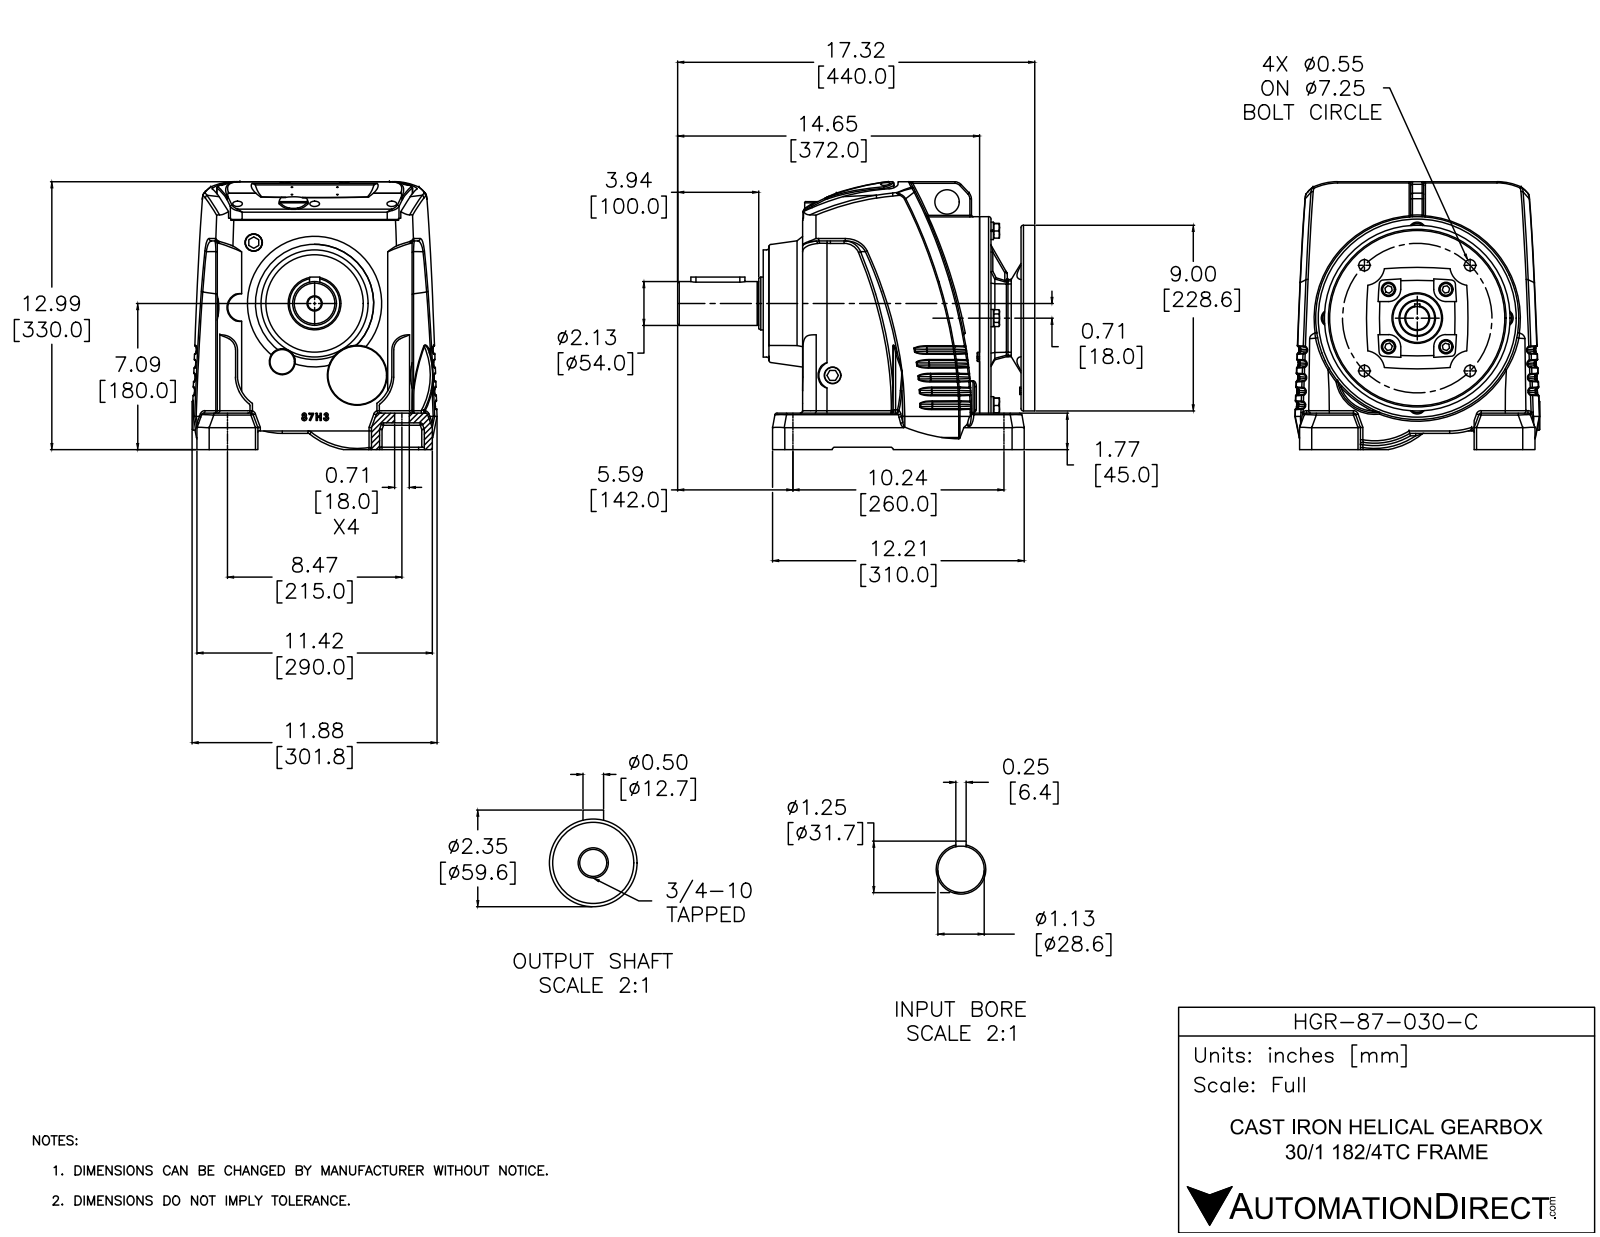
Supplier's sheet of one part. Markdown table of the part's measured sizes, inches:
| quantity | value |
| --- | --- |
| part name | HGR-87-020-C |
| STEP written by | SolidWorks 2015 (CONFIG_CONTROL_DESIGN) |
| units | inches |
| bodies | 27 solids, 1305 faces (317 planar, 298 cylindrical, 690 other) |
| overall size | 17.323 × 12.992 × 11.882 |
| volume | 1 105 in³ |
| surface area | 1 488 in² |
| round holes (diameter × count) | 0.472 × 7, 0.079 × 4, 0.551 × 4, 0.689 × 4, 0.709 × 4, 0.839 × 3, 0.656 × 1, 0.75 × 1, 0.878 × 1, 1.125 × 1, 1.181 × 1, 1.378 × 1 |
| round bosses / shafts (diameter × count) | 0.866 × 5, 0.846 × 4, 0.63 × 4, 0.394 × 4, 9.843 × 1, 9 × 1, 5.494 × 1, 5.197 × 1 |
| partial cylindrical surfaces (radius × count) | 0.118 × 60, 0.591 × 14, 0.079 × 12, 0.125 × 6, 0.394 × 4, 0.709 × 4, 0.984 × 4, 0.039 × 3 |
| main face-to-face distances | 0.039, 0.551, 8.465, 0.591, 0.394, 2.559, 9.6, 9.134, 8.583, 1.457 |
| hole center spacings | 4.125, 1.656, 1.969, 2.784, 3.625, 5.127, 5.594, 2.874 |
